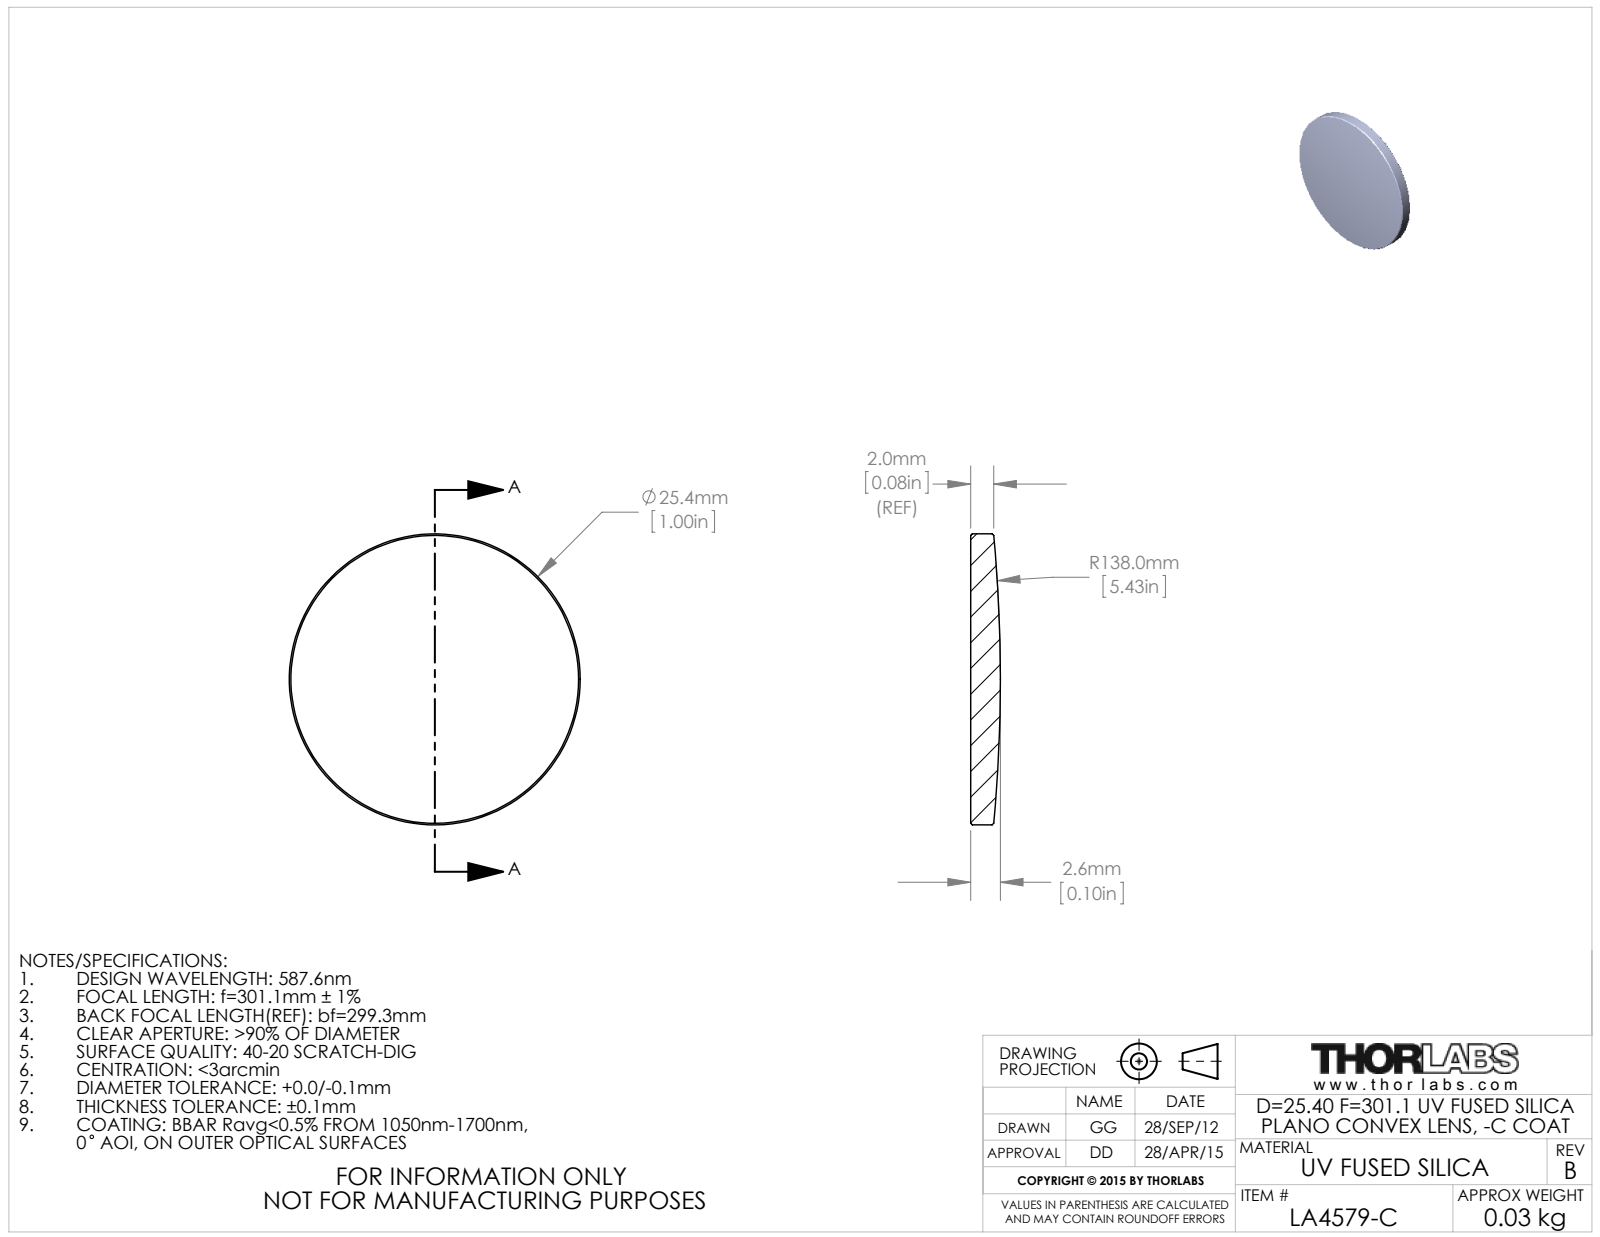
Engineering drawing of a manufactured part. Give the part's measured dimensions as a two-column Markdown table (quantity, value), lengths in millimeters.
| quantity | value |
| --- | --- |
| part name | 24995-E0W |
| STEP written by | SolidWorks 2014 (CONFIG_CONTROL_DESIGN) |
| units | millimeters |
| bodies | 1 solid, 9 faces (1 planar, 2 cylindrical, 6 other) |
| overall size | 25.4 × 25.4 × 2.59 |
| volume | 1 161 mm³ |
| surface area | 1 162 mm² |
| round bosses / shafts (diameter × count) | 25.4 × 1 |
